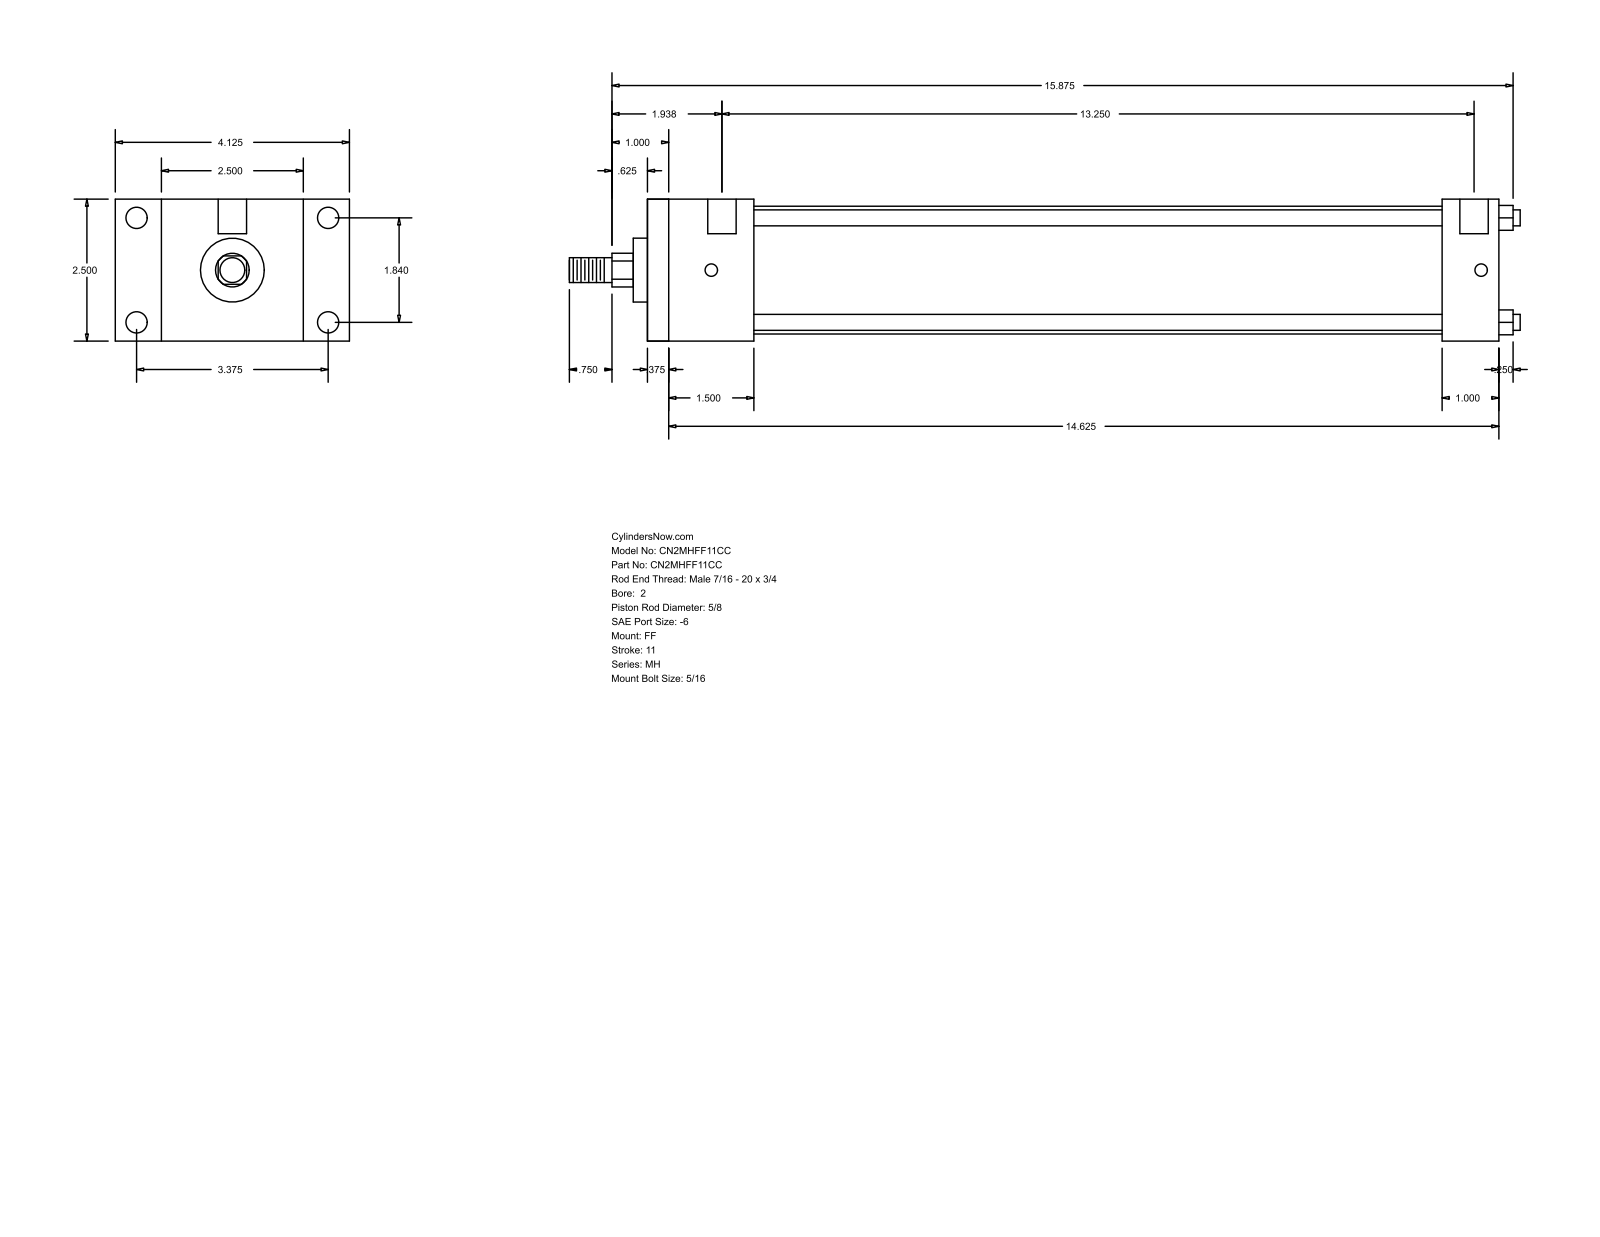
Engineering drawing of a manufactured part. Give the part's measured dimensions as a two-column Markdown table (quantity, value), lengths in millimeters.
| quantity | value |
| --- | --- |
| part name | MH_FF__0200_0.625 |
| STEP written by | GSSL Pune (CONFIG_CONTROL_DESIGN) |
| units | millimeters |
| bodies | 0 solids, 92 faces (64 planar, 28 cylindrical, 0 other) |
| overall size | 425.45 × 104.78 × 63.5 |
| round holes (diameter × count) | 5.56 × 4, 9.53 × 4, 12.7 × 2 |
| round bosses / shafts (diameter × count) | 7.14 × 4, 57.15 × 1, 28.57 × 1, 15.88 × 1, 11.11 × 1 |
| partial cylindrical surfaces (radius × count) | 7.54 × 1 |
| main face-to-face distances | 63.5, 381, 9.52, 371.48, 25.4, 38.1, 47.62, 355.6, 346.08, 307.98 |
| hole center spacings | 46.74, 85.72, 97.63, 344.49, 3.18, 4.76, 336.55, 339.73 |
